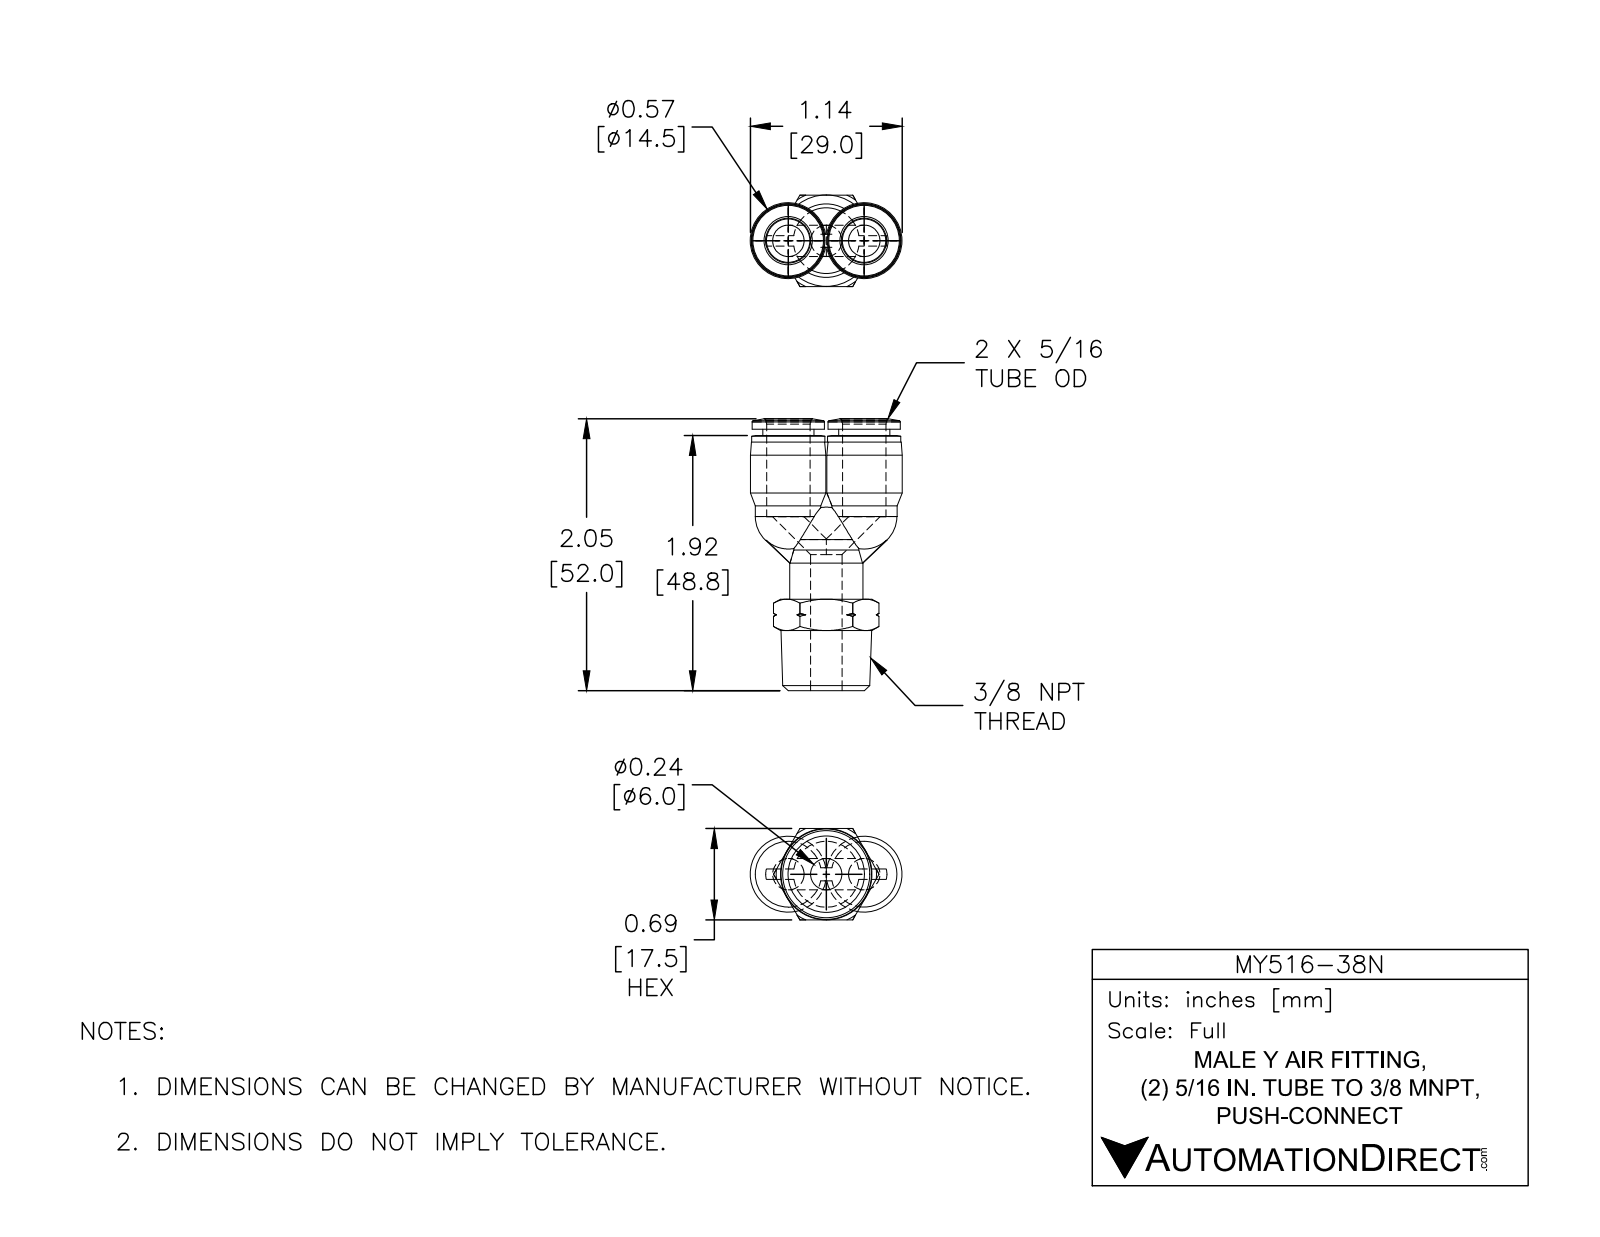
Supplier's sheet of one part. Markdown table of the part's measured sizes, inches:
| quantity | value |
| --- | --- |
| part name | MY516-38N |
| STEP written by | SolidWorks 2015 (CONFIG_CONTROL_DESIGN) |
| units | inches |
| bodies | 1 solid, 127 faces (22 planar, 31 cylindrical, 74 other) |
| overall size | 2.045 × 1.142 × 0.687 |
| volume | 0.579 in³ |
| surface area | 9.275 in² |
| round holes (diameter × count) | 0.327 × 2, 0.236 × 1 |
| round bosses / shafts (diameter × count) | 0.551 × 3, 0.496 × 3, 0.571 × 2, 0.543 × 2, 0.386 × 2 |
| main face-to-face distances | 0.687, 1.967, 1.919, 0.047, 0.689, 1.23, 1.278, 1.309, 0.62, 0.61 |
| hole center spacings | 0.285, 0.571 |
